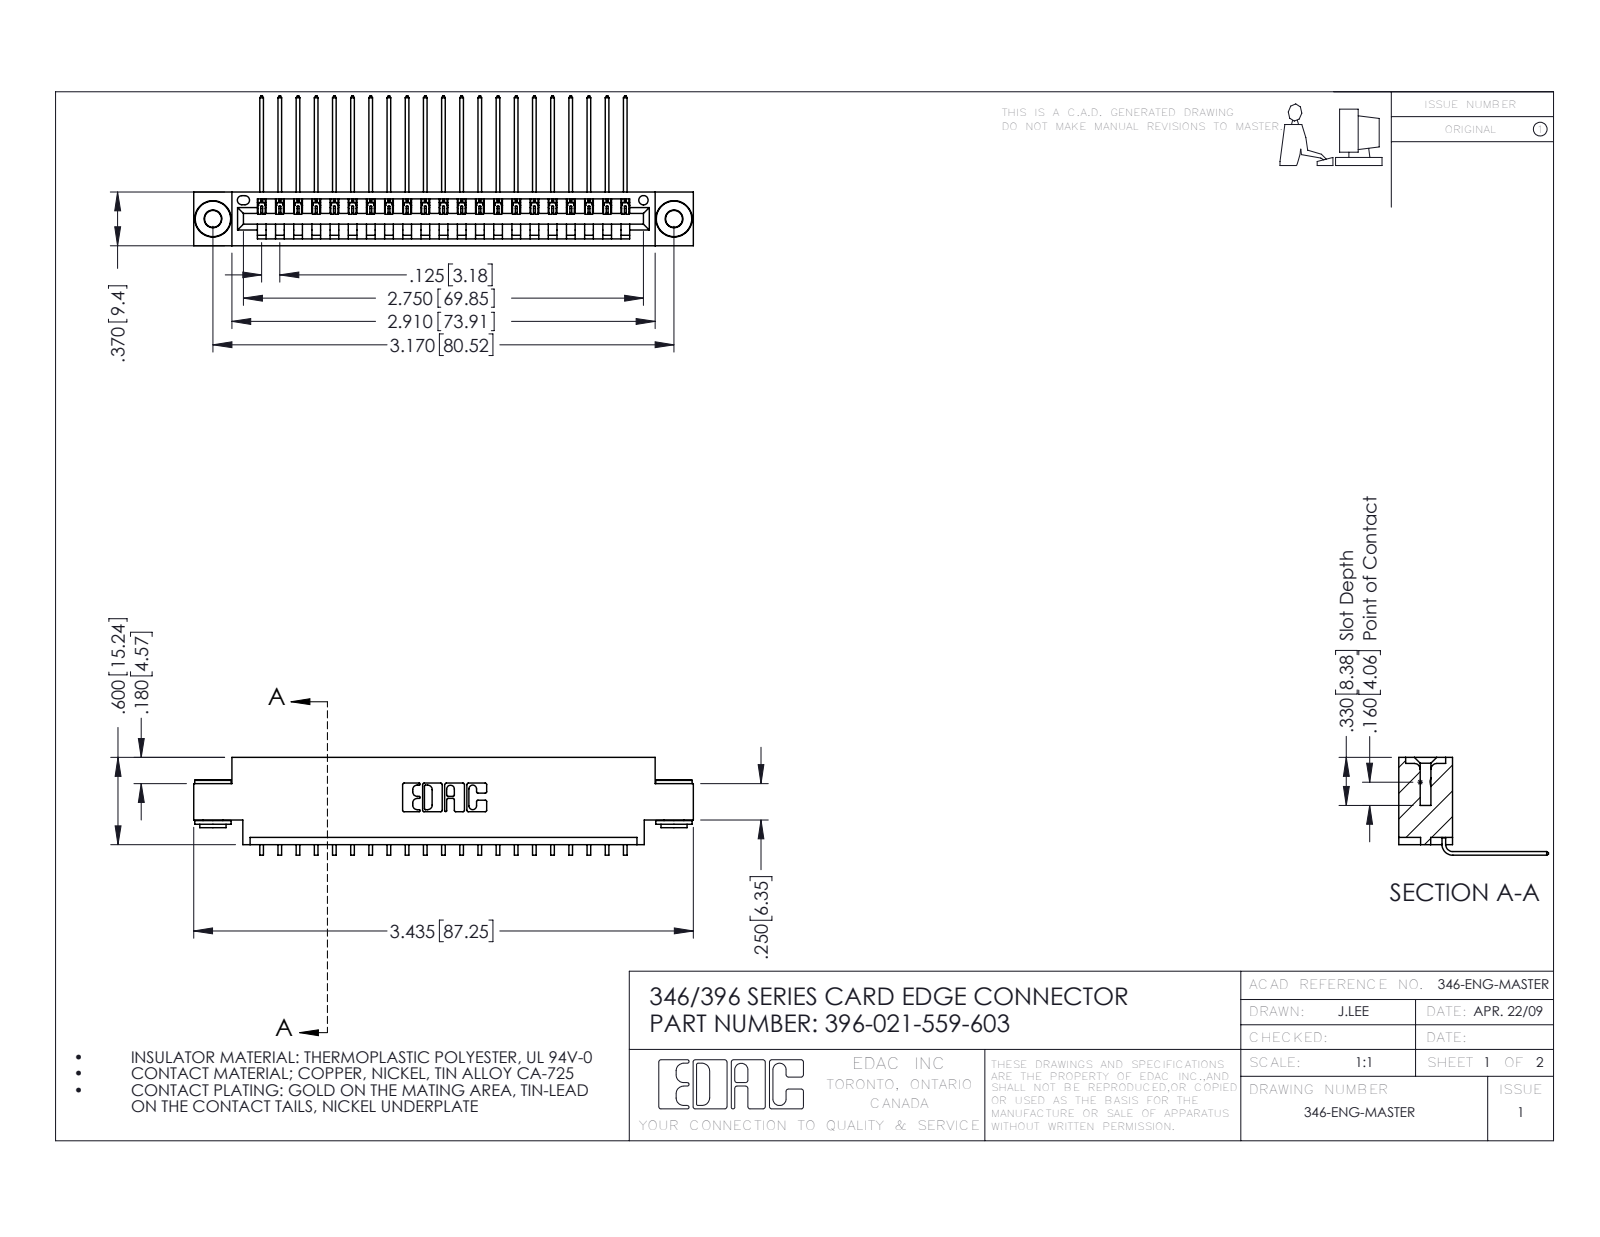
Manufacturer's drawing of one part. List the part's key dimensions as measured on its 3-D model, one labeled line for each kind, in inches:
Part name (STEP PRODUCT): 396-021-559-603; 346 Part_0.170 Offset - 0.156 Dia-TH; 345-292-001_558 559 Tail - 1; 345-250-002_345-250-002-102
STEP written by: SolidWorks 2016 (CONFIG_CONTROL_DESIGN)
Units: inches
Bodies: 24 solids, 1424 faces (972 planar, 444 cylindrical, 8 other)
Overall size (bounding box): 3.435 × 1.03 × 0.673
Volume: 0.497 in³ · Surface area: 16.66 in²
Round holes (diameter × count): ⌀0.116 ×2, ⌀0.156 ×2, ⌀0.064 ×1
Round bosses / shafts (diameter × count): ⌀0.25 ×2, ⌀0.18 ×2, ⌀0.136 ×2
Partial cylindrical surfaces — rounded edges, fillets, slot ends (radius × count): R0.006 ×42, R0.01 ×22, R0.007 ×6, R0.031 ×6, R0.026 ×3, R0.031 ×2, R0.04 ×2, R0.014 ×1
Main face-to-face distances: 0.048, 0.37, 0.322, 0.25, 0.025, 0.072, 0.148, 0.222, 0.1, 0.174
Hole centre spacings: 0.246, 2.963, 3.17
